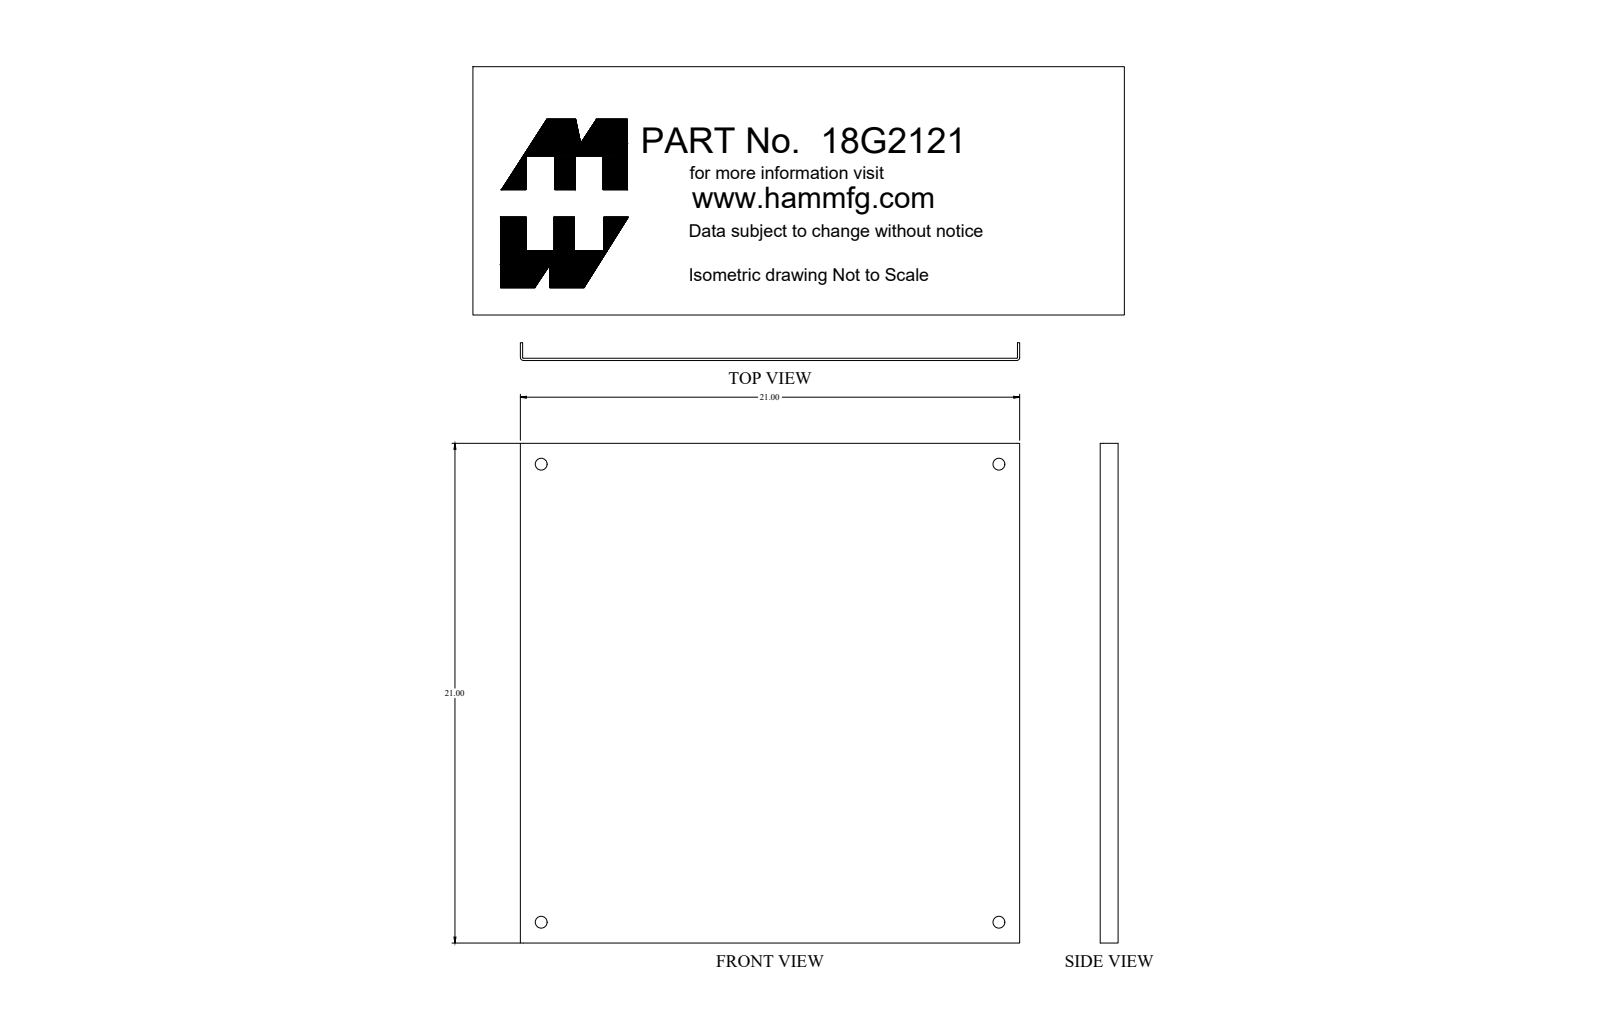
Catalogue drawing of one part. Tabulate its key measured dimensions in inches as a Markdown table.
| quantity | value |
| --- | --- |
| part name | 18G2121 |
| STEP written by | SolidWorks 2018 (AUTOMOTIVE_DESIGN) |
| units | inches |
| bodies | 1 solid, 18 faces (10 planar, 8 cylindrical, 0 other) |
| overall size | 21 × 21 × 0.75 |
| volume | 44.3 in³ |
| surface area | 941.5 in² |
| round holes (diameter × count) | 0.5 × 4 |
| partial cylindrical surfaces (radius × count) | 0.03 × 2, 0.125 × 2 |
| main face-to-face distances | 0.095, 20.905, 21, 20.81, 0.75, 0.655 |
| hole center spacings | 19.25, 27.223 |
